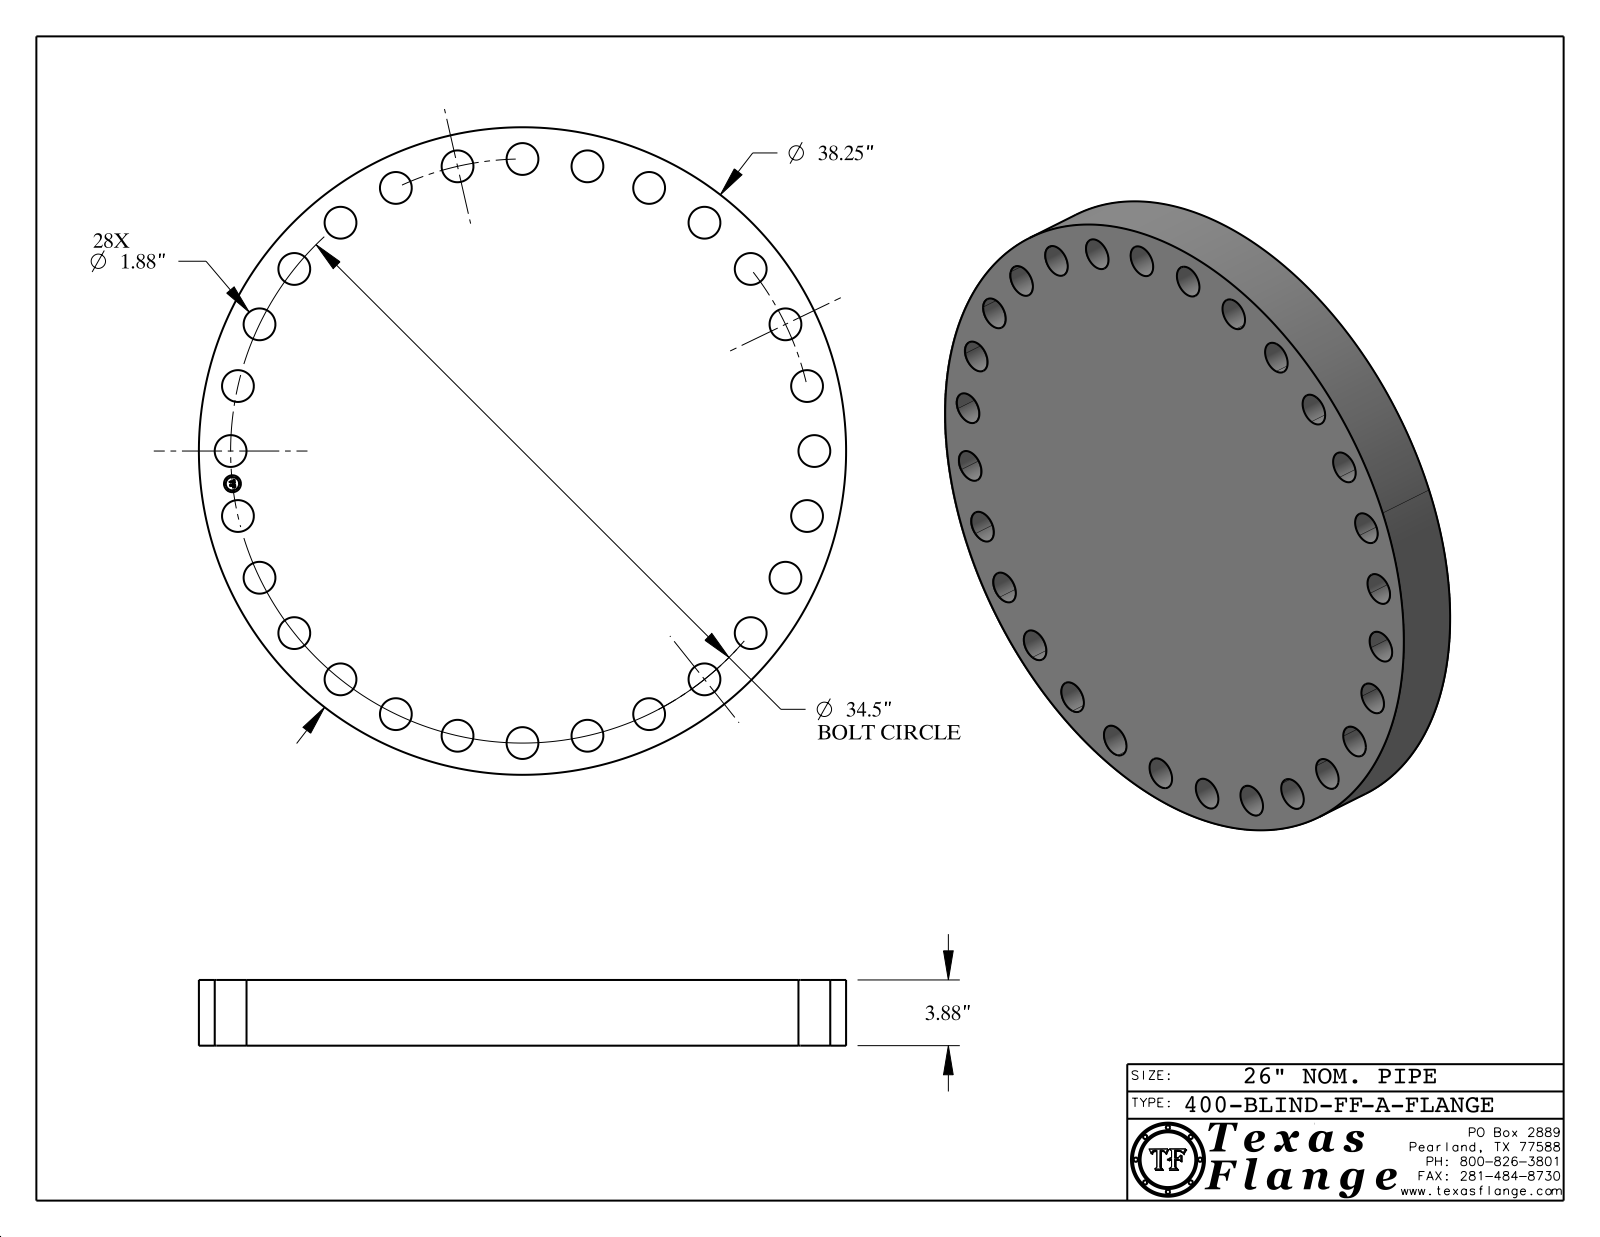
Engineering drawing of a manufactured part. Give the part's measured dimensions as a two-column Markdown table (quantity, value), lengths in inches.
| quantity | value |
| --- | --- |
| part name | 400-BLIND-FF, Series A |
| STEP written by | CATIA V5 STEP AP214 (AUTOMOTIVE_DESIGN) |
| units | inches |
| bodies | 1 solid, 445 faces (367 planar, 78 cylindrical, 0 other) |
| overall size | 38.25 × 38.25 × 3.88 |
| volume | 4 157 in³ |
| surface area | 3 251 in² |
| round holes (diameter × count) | 1.88 × 28, 1 × 1 |
| round bosses / shafts (diameter × count) | 0.061 × 8, 38.25 × 1, 0.788 × 1 |
| main face-to-face distances | 3.88, 0.015, 3.865, 0.298, 0.292, 0.054, 0.193, 0.248, 0.044, 0.15 |
| hole center spacings | 26.973, 34.283, 14.969, 18.355, 32.564, 33.635, 11.394, 21.51 |
